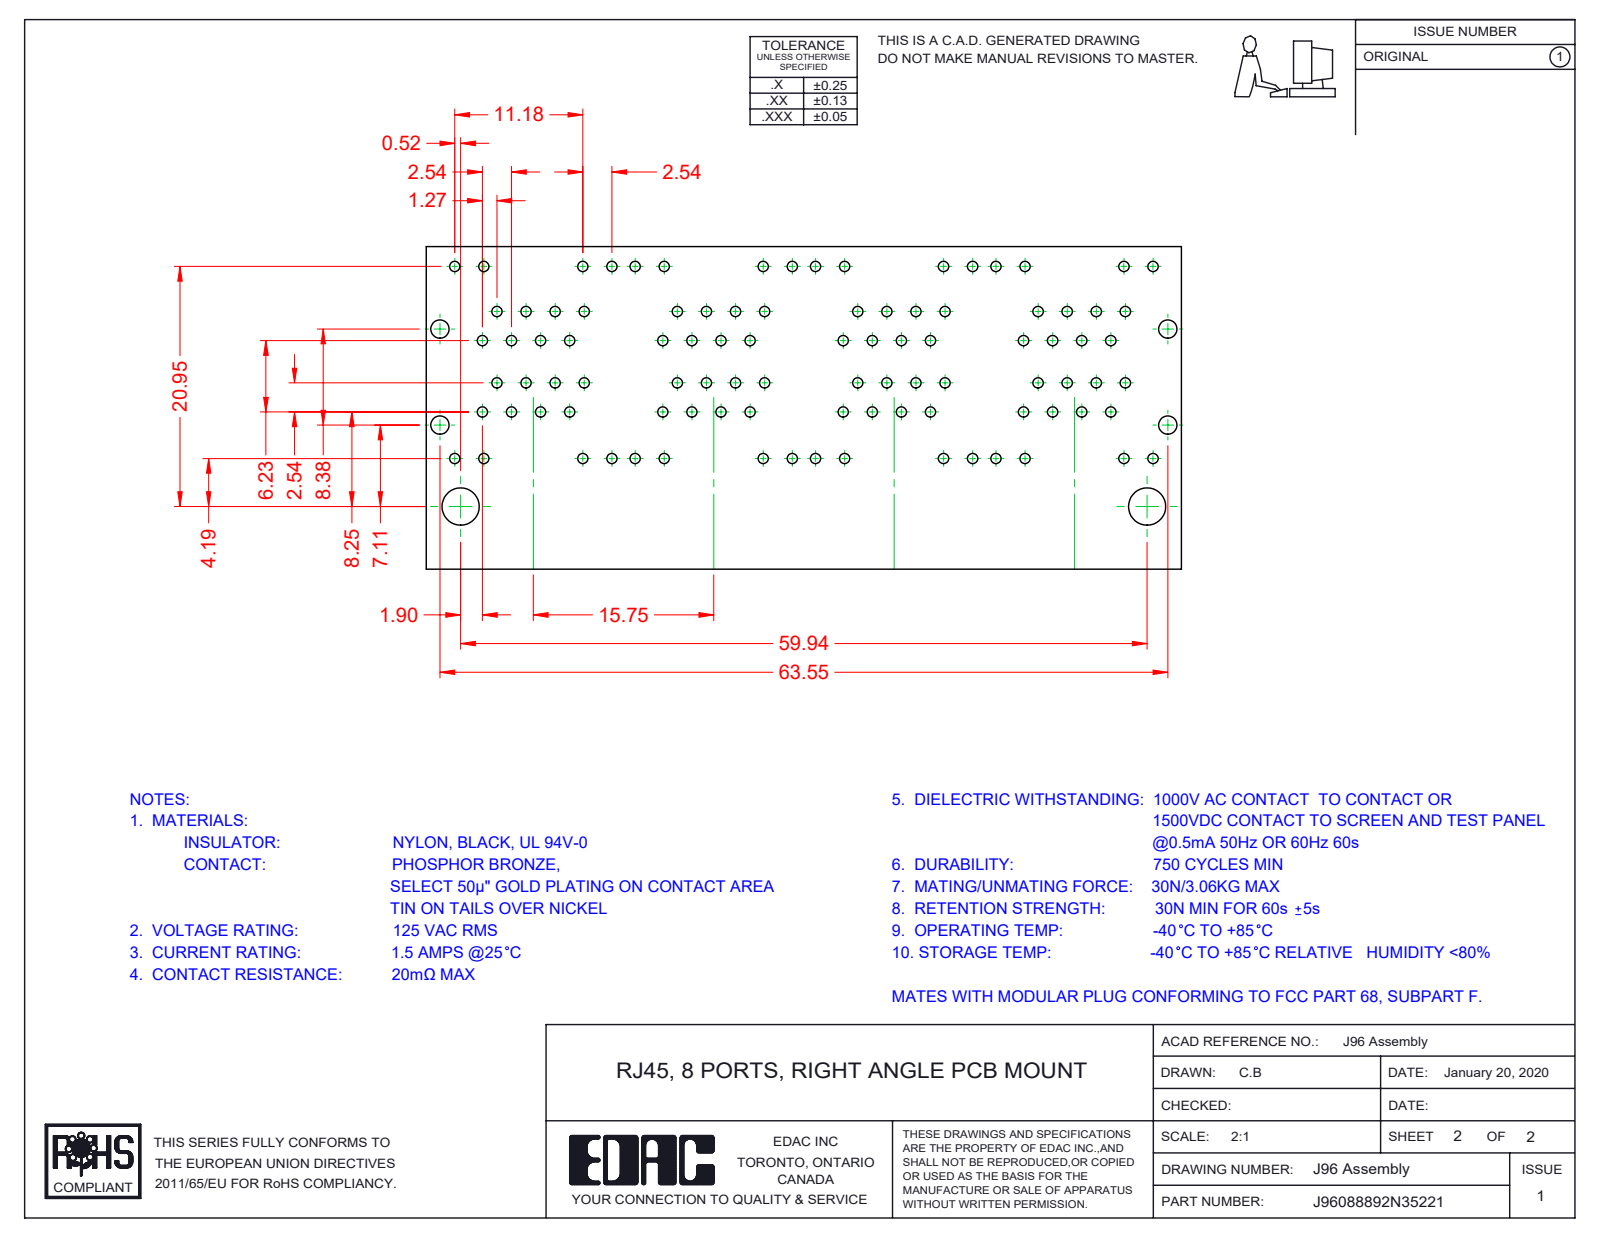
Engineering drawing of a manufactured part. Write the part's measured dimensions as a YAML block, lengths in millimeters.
part_name: "96 LED RH Lower_5-Green-Yellow; 96 LED LH Lower_3-Green; 96 Insulator Insert; 96 Insulator_8 Ports (+8 more)"
step_written_by: "SolidWorks 2016 (CONFIG_CONTROL_DESIGN)"
units: millimeters
bodies: {solids: 96, faces: 7820, planar: 6105, cylindrical: 1404, other: 311}
overall_size: [67.35, 31.38, 28.68]
volume: 24149
surface_area: 63596
round_holes:
  - {diameter: 1.7, count: 3}
round_bosses_or_shafts:
  - {diameter: 1.68, count: 3}
partial_cylinders:
  - {radius: 0.25, count: 124}
  - {radius: 0.35, count: 73}
  - {radius: 1, count: 72}
  - {radius: 0.5, count: 49}
  - {radius: 0.91, count: 32}
  - {radius: 0.2, count: 27}
  - {radius: 0.27, count: 14}
  - {radius: 0.7, count: 11}
face_to_face_distances: [15.75, 0.35, 9.95, 1.17, 1.6, 0.54, 9.98, 10.18, 12.67, 3.37]
hole_center_spacings: [15.75, 31.5]
